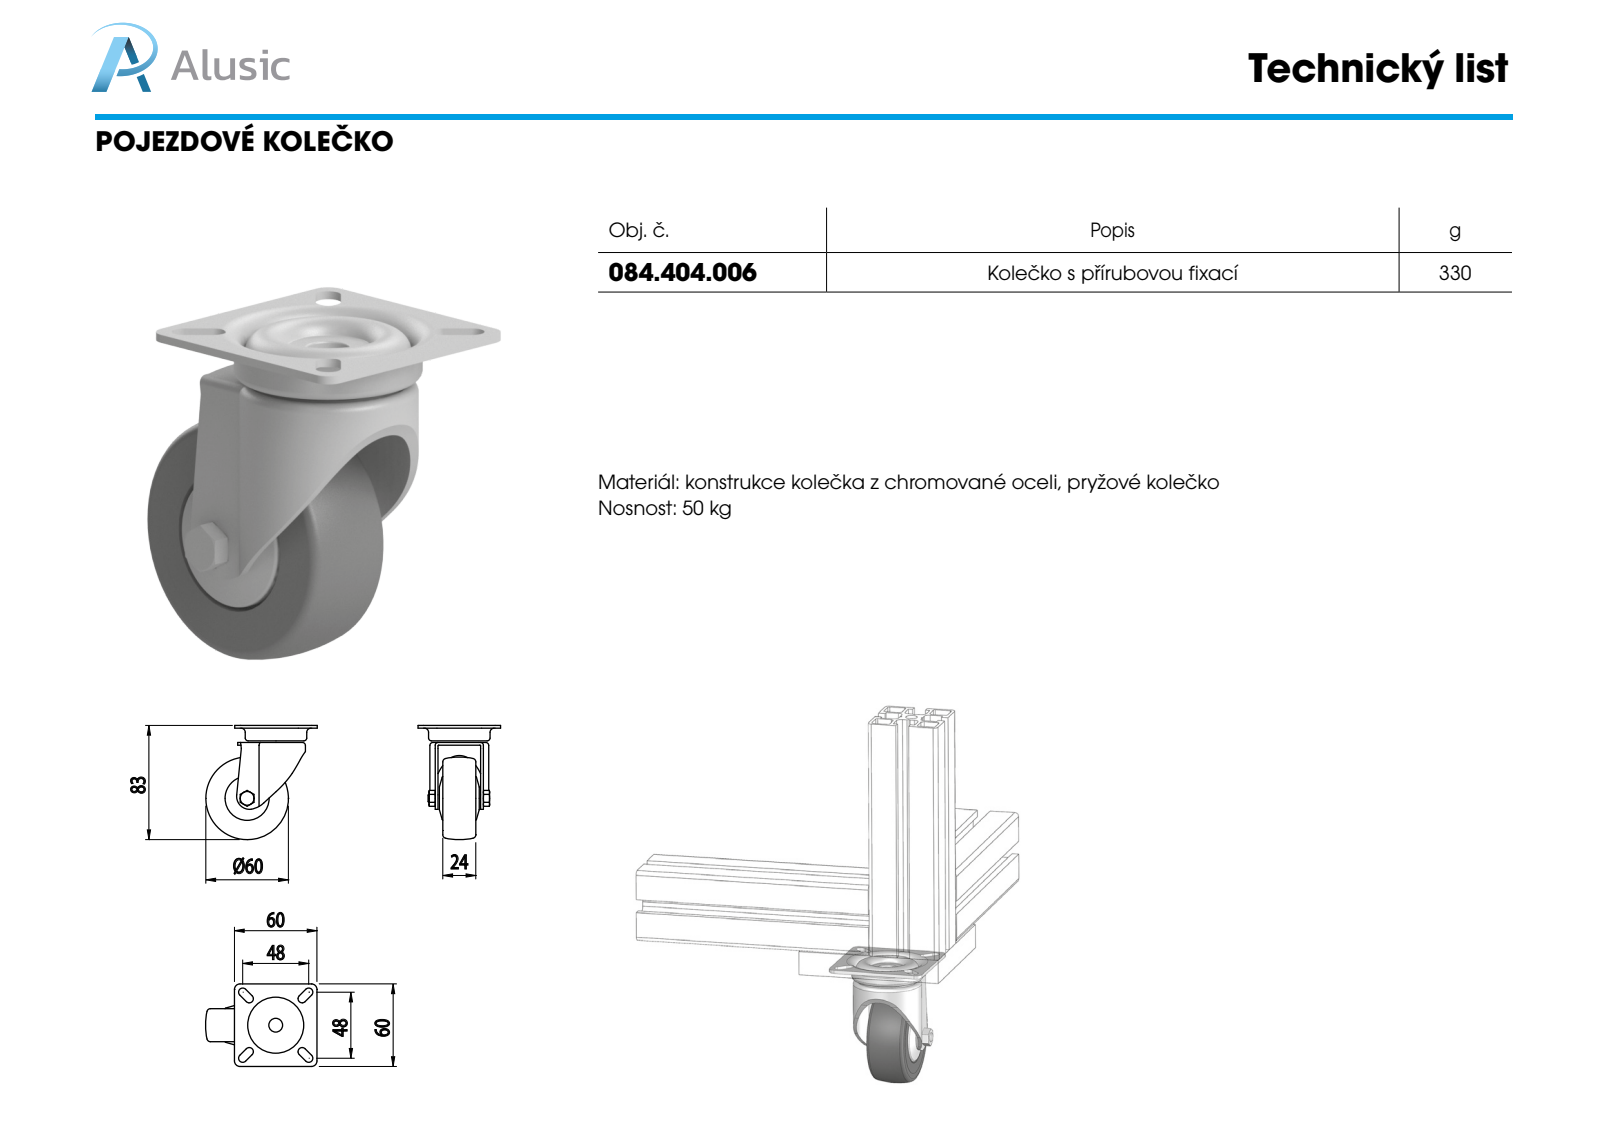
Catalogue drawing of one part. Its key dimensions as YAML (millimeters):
part_name: "084.404.006"
step_written_by: "SolidWorks 2011 (CONFIG_CONTROL_DESIGN)"
units: millimeters
bodies: {solids: 0, faces: 182, planar: 55, cylindrical: 64, other: 63}
overall_size: [82.98, 81, 60]
round_holes:
  - {diameter: 10.02, count: 1}
  - {diameter: 34, count: 1}
  - {diameter: 34, count: 1}
  - {diameter: 40.72, count: 1}
  - {diameter: 46.74, count: 1}
round_bosses_or_shafts:
  - {diameter: 46.7, count: 1}
  - {diameter: 44.72, count: 1}
  - {diameter: 39.72, count: 1}
  - {diameter: 32, count: 1}
  - {diameter: 31.72, count: 1}
  - {diameter: 6, count: 1}
partial_cylinders:
  - {radius: 3, count: 8}
  - {radius: 4, count: 4}
  - {radius: 0.5, count: 2}
  - {radius: 2, count: 2}
  - {radius: 9.42, count: 1}
  - {radius: 18.1, count: 1}
  - {radius: 19.4, count: 1}
  - {radius: 21.4, count: 1}
face_to_face_distances: [2, 12.38, 3.5, 27.5, 24, 5.5, 29.5, 33, 10.38, 31]
